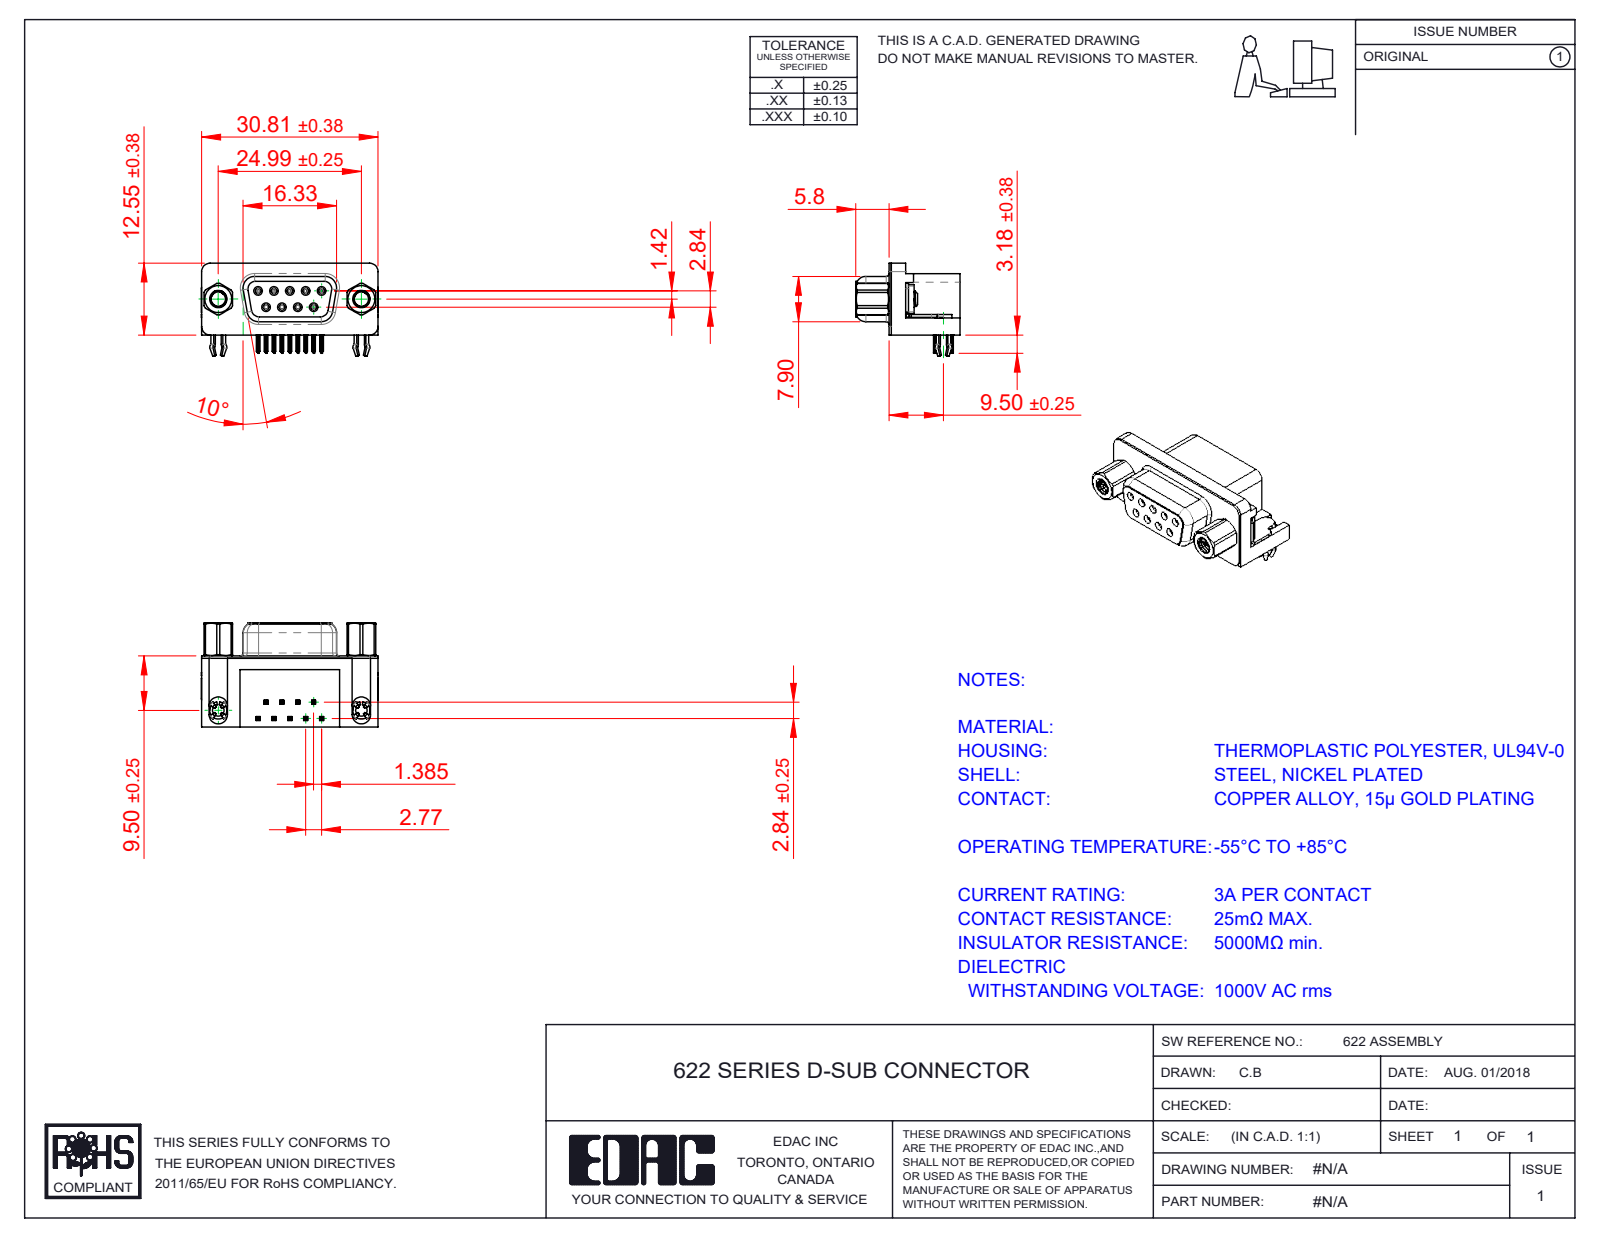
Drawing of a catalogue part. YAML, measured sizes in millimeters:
part_name: "622-009-360-056; 622 Housing_9 Socket; 622 M3 Threaded Rivet; 622 Shell_9 Socket (+3 more)"
step_written_by: "SolidWorks 2016 (CONFIG_CONTROL_DESIGN)"
units: millimeters
bodies: {solids: 15, faces: 1602, planar: 684, cylindrical: 432, other: 486}
overall_size: [30.89, 18.2, 15.73]
volume: 3732
surface_area: 5156
round_holes:
  - {diameter: 0.8, count: 9}
  - {diameter: 0.9, count: 9}
  - {diameter: 2.26, count: 2}
  - {diameter: 2.5, count: 2}
  - {diameter: 4, count: 2}
  - {diameter: 4.8, count: 2}
  - {diameter: 5, count: 2}
round_bosses_or_shafts:
  - {diameter: 1.2, count: 9}
  - {diameter: 4.9, count: 2}
  - {diameter: 4.75, count: 2}
  - {diameter: 3.9, count: 2}
  - {diameter: 3.26, count: 2}
partial_cylinders:
  - {radius: 0.1, count: 72}
  - {radius: 0.15, count: 36}
  - {radius: 0.35, count: 18}
  - {radius: 1, count: 18}
  - {radius: 0.34, count: 9}
  - {radius: 0.25, count: 8}
  - {radius: 1.35, count: 8}
  - {radius: 1.6, count: 8}
face_to_face_distances: [0.4, 12, 12.4, 0.35, 2.9, 2.5, 6.2, 10.34, 9.5, 5.8]
hole_center_spacings: [3.16, 2.77, 5.54, 5.03, 5.04, 8.31, 7.48, 7.49]
